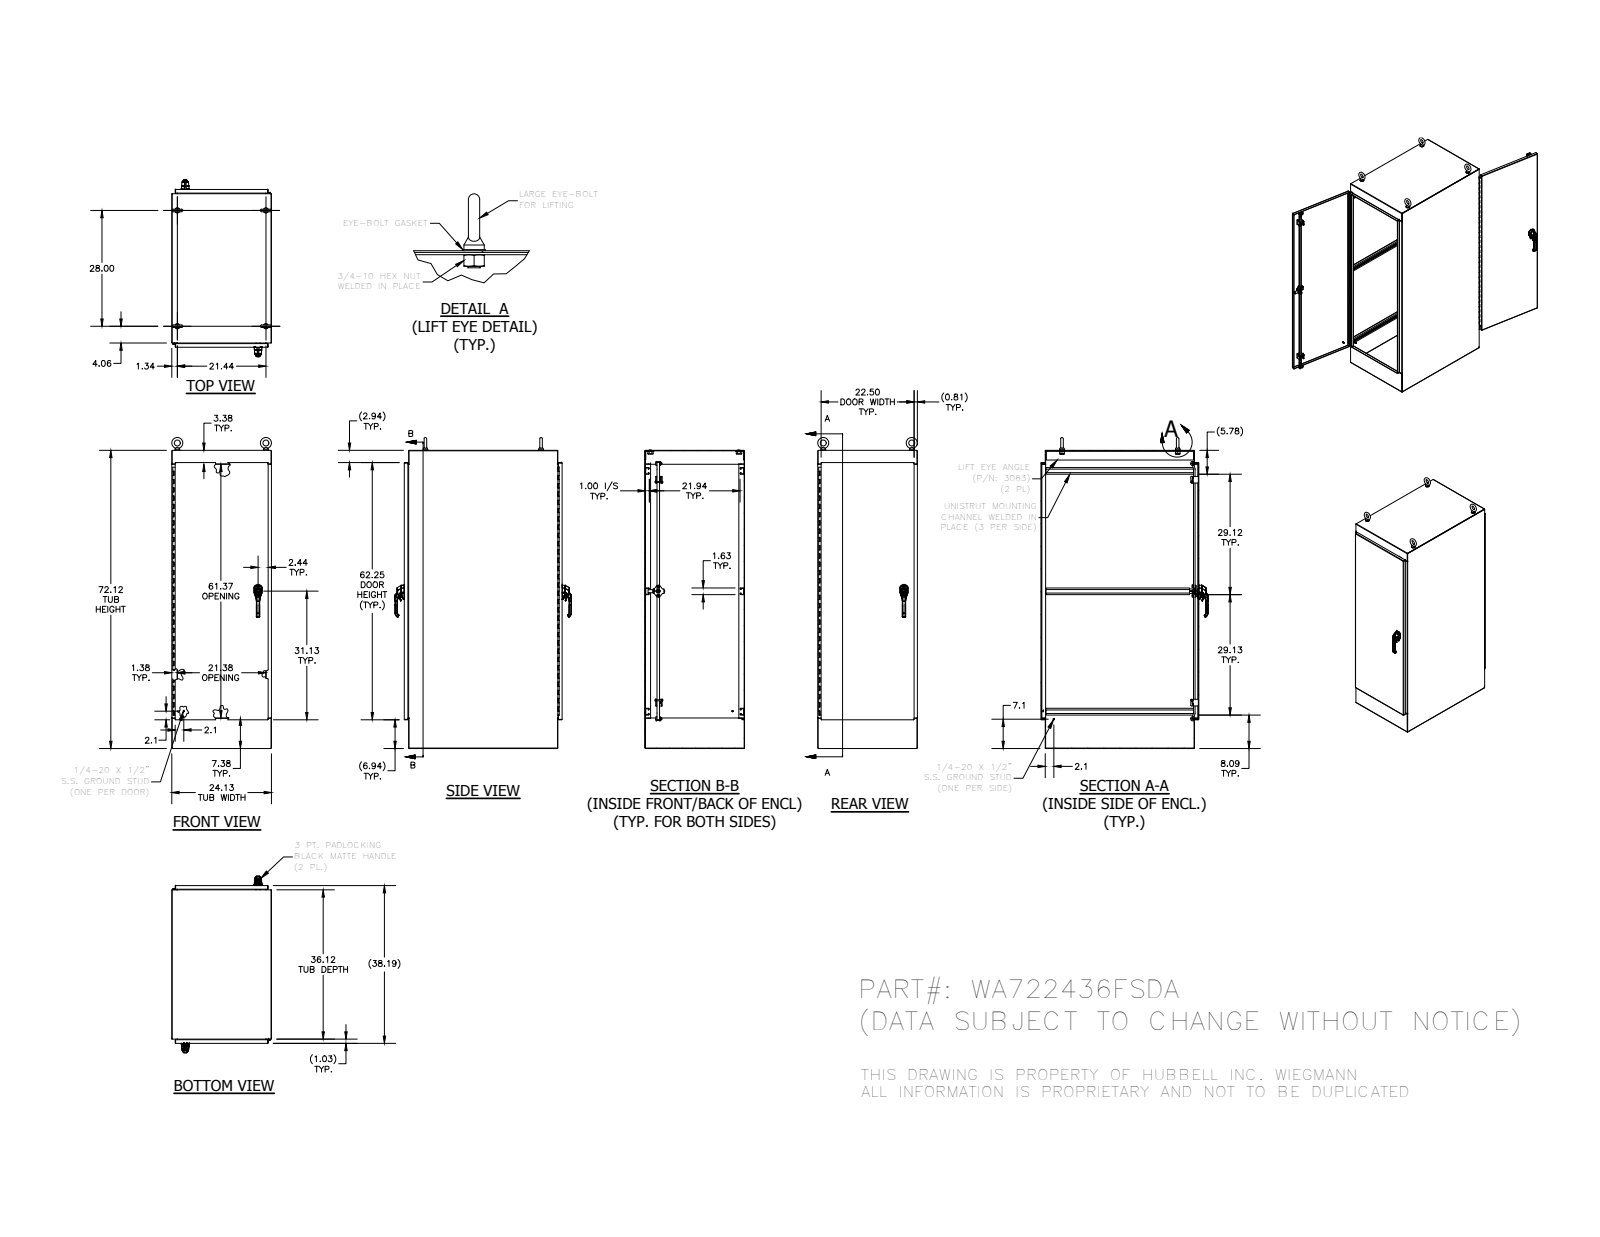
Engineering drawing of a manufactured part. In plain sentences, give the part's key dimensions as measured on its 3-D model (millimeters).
The part is named "WA7236FSDALRS; WA2436FSDABTM; WA2436FSDATOP; WA7224FSDADR (+8 more)". Its 3-D file was written by "Autodesk Inventor 2014 (AUTOMOTIVE_DESIGN)". It is 90 solids with 5786 faces: 2392 planar, 2036 cylindrical and 1358 other. Overall it measures 1911.29 by 1085.21 by 612.77 millimeters. Its volume is 19 860 000 cubic millimeters and its surface area 16 810 000 square millimeters. Round holes: 16 of diameter 7.02, 8 of diameter 5.08, 6 of diameter 5.4, 6 of diameter 6, 6 of diameter 7.11, 4 of diameter 6.13, 4 of diameter 6.35, 4 of diameter 6.41, 4 of diameter 10.16, 4 of diameter 10.33, 4 of diameter 10.5, 4 of diameter 11.43. Round bosses or shafts: 6 of diameter 6.35, 4 of diameter 31.75, 4 of diameter 28.45, 4 of diameter 25.4, 4 of diameter 19.05, 4 of diameter 14.29, 4 of diameter 13.37, 4 of diameter 12.7. Partial cylindrical surfaces (rounded edges, fillets, slot ends): 332 of radius 0.5, 169 of radius 0.3, 38 of radius 0.47, 32 of radius 0.25, 30 of radius 2, 28 of radius 1.27, 26 of radius 0.79, 24 of radius 3. The main face-to-face distances are 2.38, 610.4, 608.02, 967.59, 612.78, 1829.59, 965.21, 969.97, 1827.21, 1831.97. The hole center spacings are 447.64, 9.66, 9.7, 9.71, 12.5, 19.36, 19.4, 22.5.
